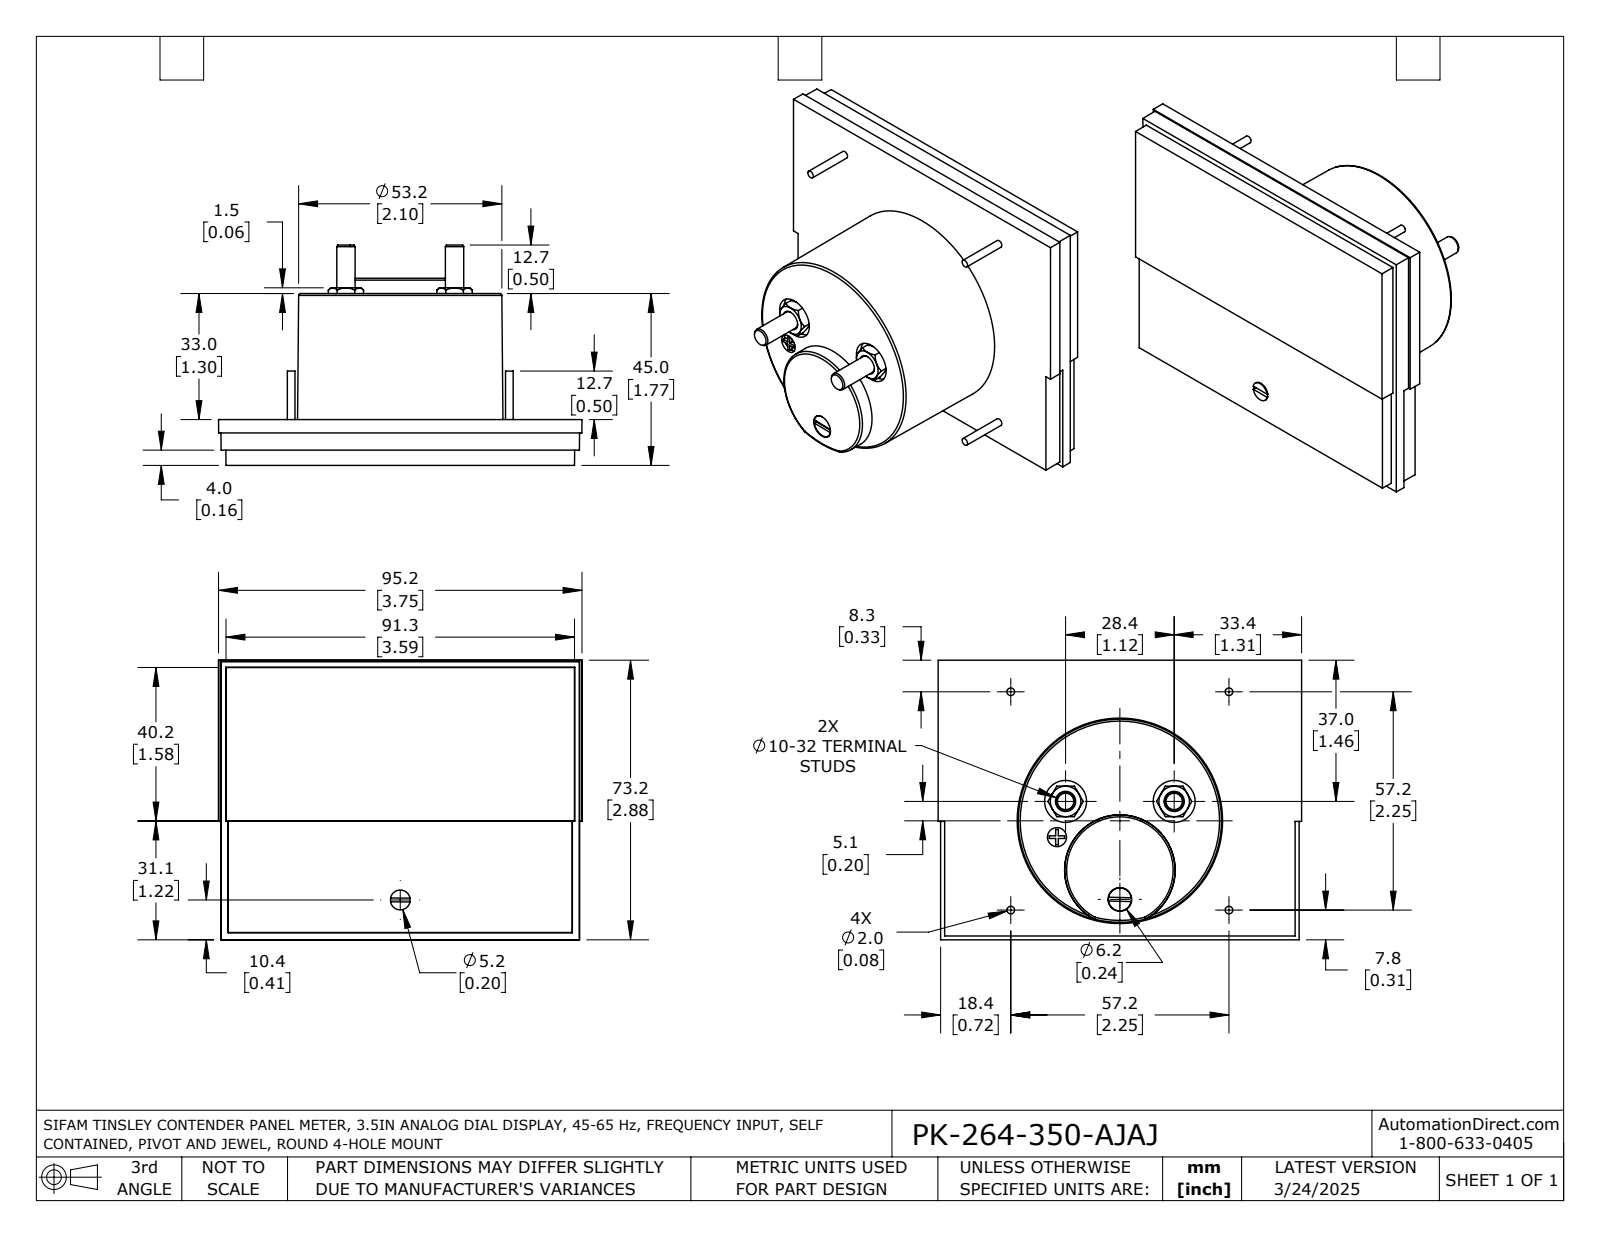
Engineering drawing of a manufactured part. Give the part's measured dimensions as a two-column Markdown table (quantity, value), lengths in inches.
| quantity | value |
| --- | --- |
| part name | PK-264-350-AJAJ |
| STEP written by | SolidWorks 2021 (AUTOMOTIVE_DESIGN) |
| units | inches |
| bodies | 1 solid, 163 faces (76 planar, 31 cylindrical, 56 other) |
| overall size | 3.748 × 2.882 × 2.272 |
| volume | 9.446 in³ |
| surface area | 38.39 in² |
| round holes (diameter × count) | 0.433 × 2, 0.197 × 1, 0.244 × 1 |
| round bosses / shafts (diameter × count) | 0.079 × 4, 0.189 × 2, 0.236 × 1, 0.205 × 1 |
| partial cylindrical surfaces (radius × count) | 0.1 × 1 |
| main face-to-face distances | 0.472, 0.03, 0.443, 1.772, 1.299, 1.742, 0.157, 0.073, 0.315, 1.457 |
| hole center spacings | 1.155, 0.379, 0.912, 1.12, 1.263 |
